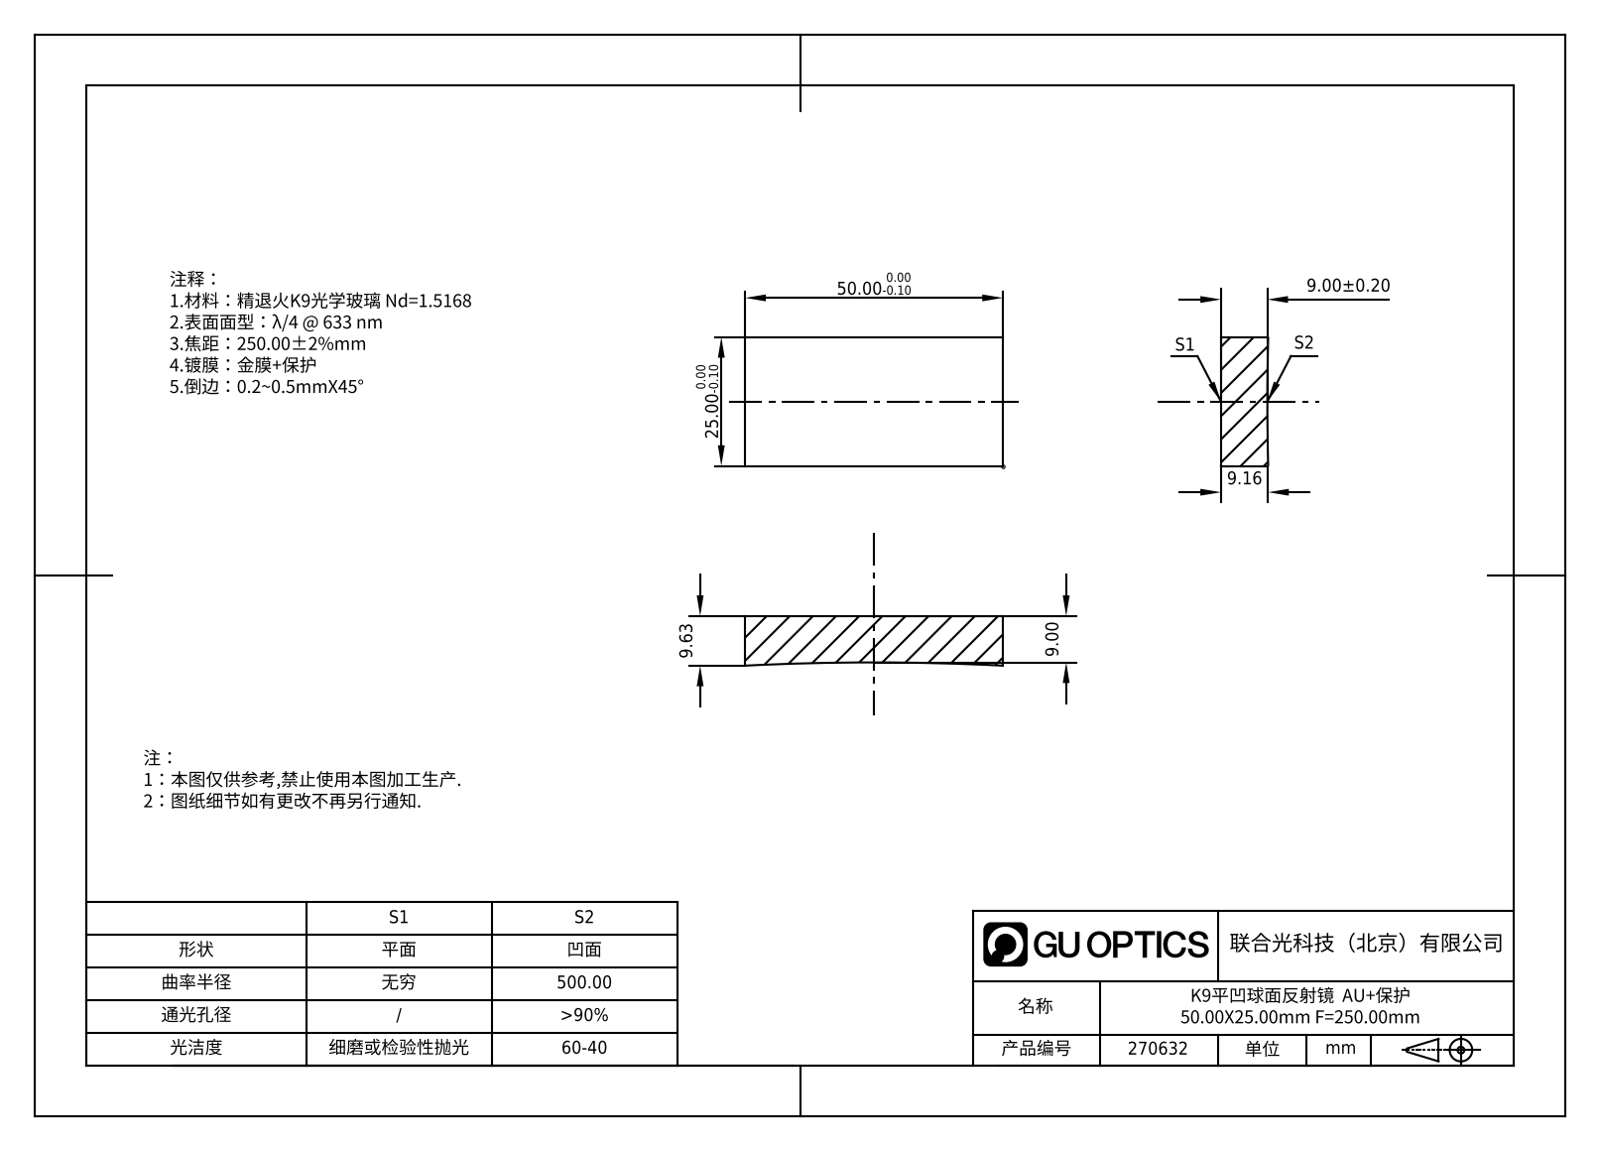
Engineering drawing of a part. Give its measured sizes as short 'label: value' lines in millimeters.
name: GM13-50x25-250
written by: SolidWorks 2022 (AUTOMOTIVE_DESIGN)
unit: mm
bodies: 1 solid, 7 faces (5 planar, 0 cylindrical, 2 other)
size: 50 × 25 × 9.78
volume: 11 576 mm³; area: 3 921 mm²
face distances: 25, 50
